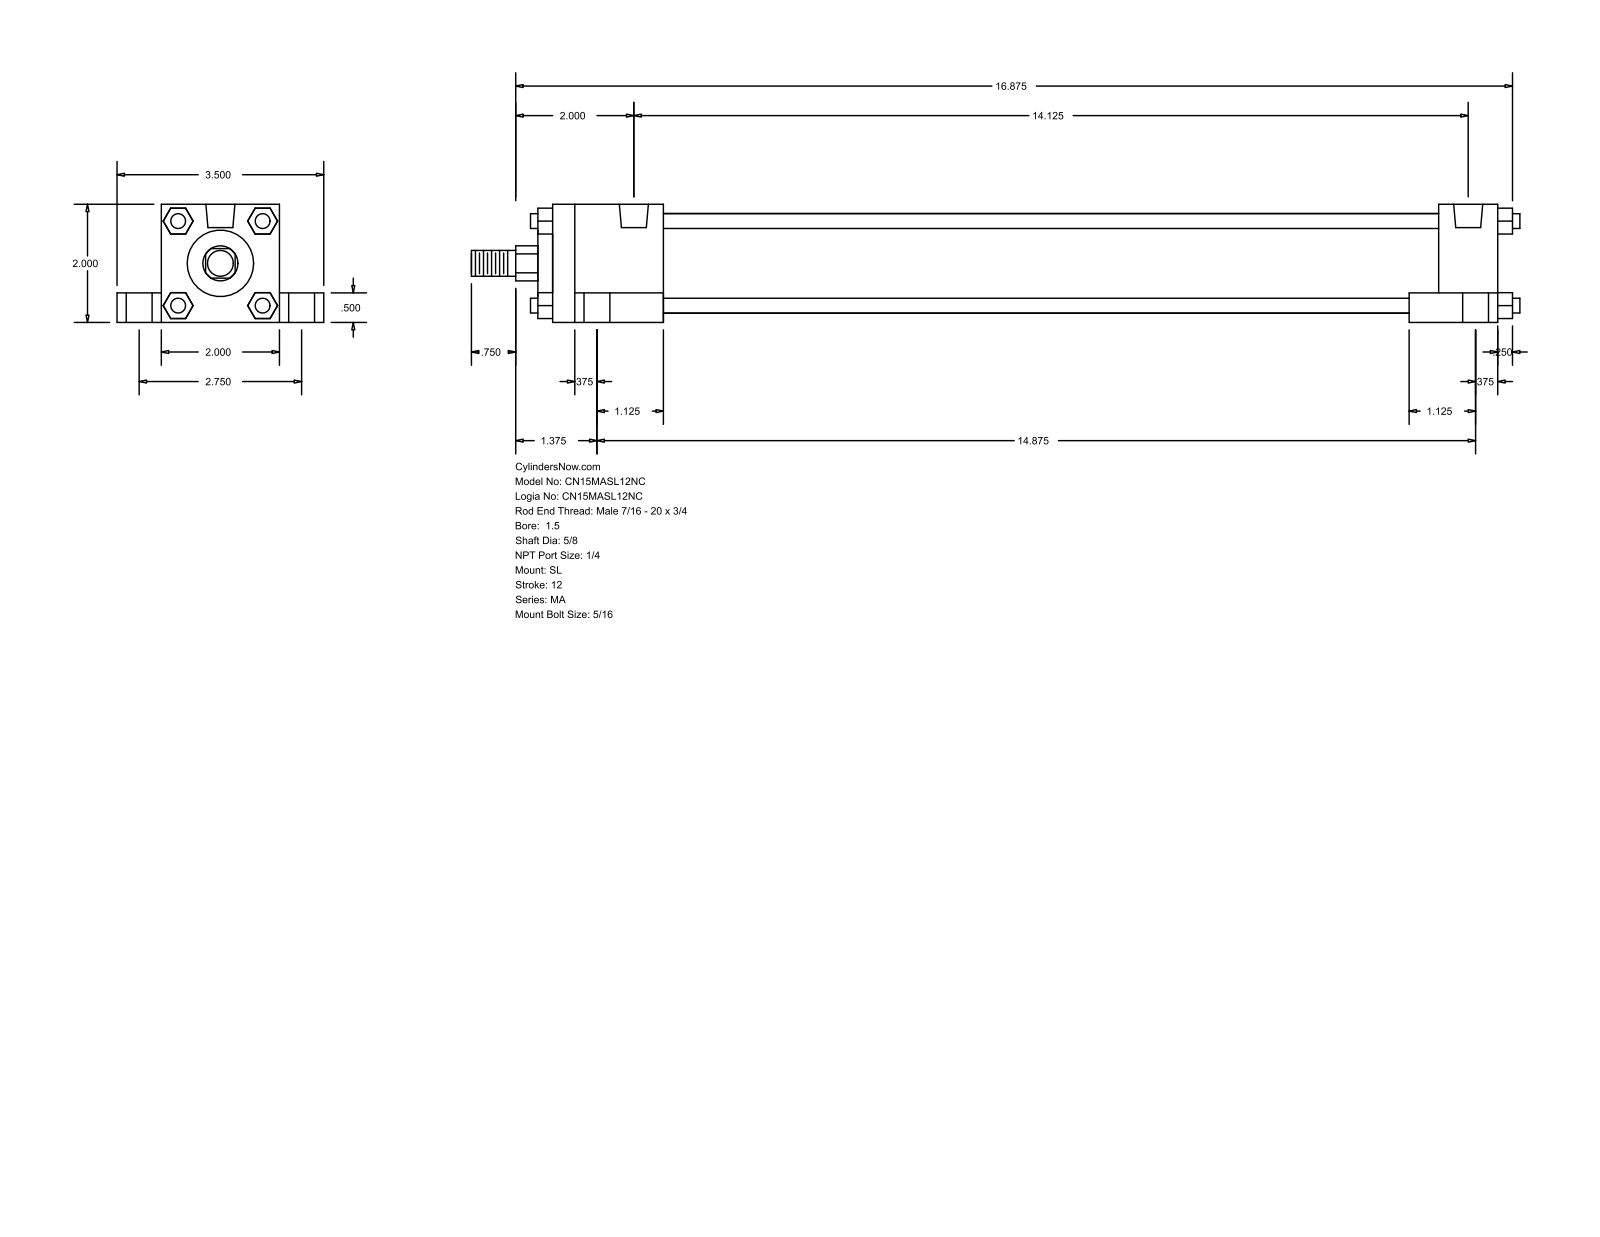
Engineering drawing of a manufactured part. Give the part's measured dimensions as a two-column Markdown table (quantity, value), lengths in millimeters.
| quantity | value |
| --- | --- |
| part name | MA_SL__0150_0.625 |
| STEP written by | GSSL Pune (CONFIG_CONTROL_DESIGN) |
| units | millimeters |
| bodies | 0 solids, 148 faces (112 planar, 36 cylindrical, 0 other) |
| overall size | 450.85 × 88.9 × 50.8 |
| round holes (diameter × count) | 7.94 × 4, 11.11 × 4, 17.46 × 4, 12.49 × 2 |
| round bosses / shafts (diameter × count) | 6.35 × 4, 42.93 × 1, 28.57 × 1, 15.88 × 1, 11.11 × 1 |
| partial cylindrical surfaces (radius × count) | 7.54 × 1 |
| main face-to-face distances | 50.8, 19.05, 38.1, 69.85, 12.7, 406.39, 6.35, 9.52, 412.74, 381 |
| hole center spacings | 35.06, 38.36, 69.84, 358.77, 363.63, 376.27, 377.83, 384.23 |
